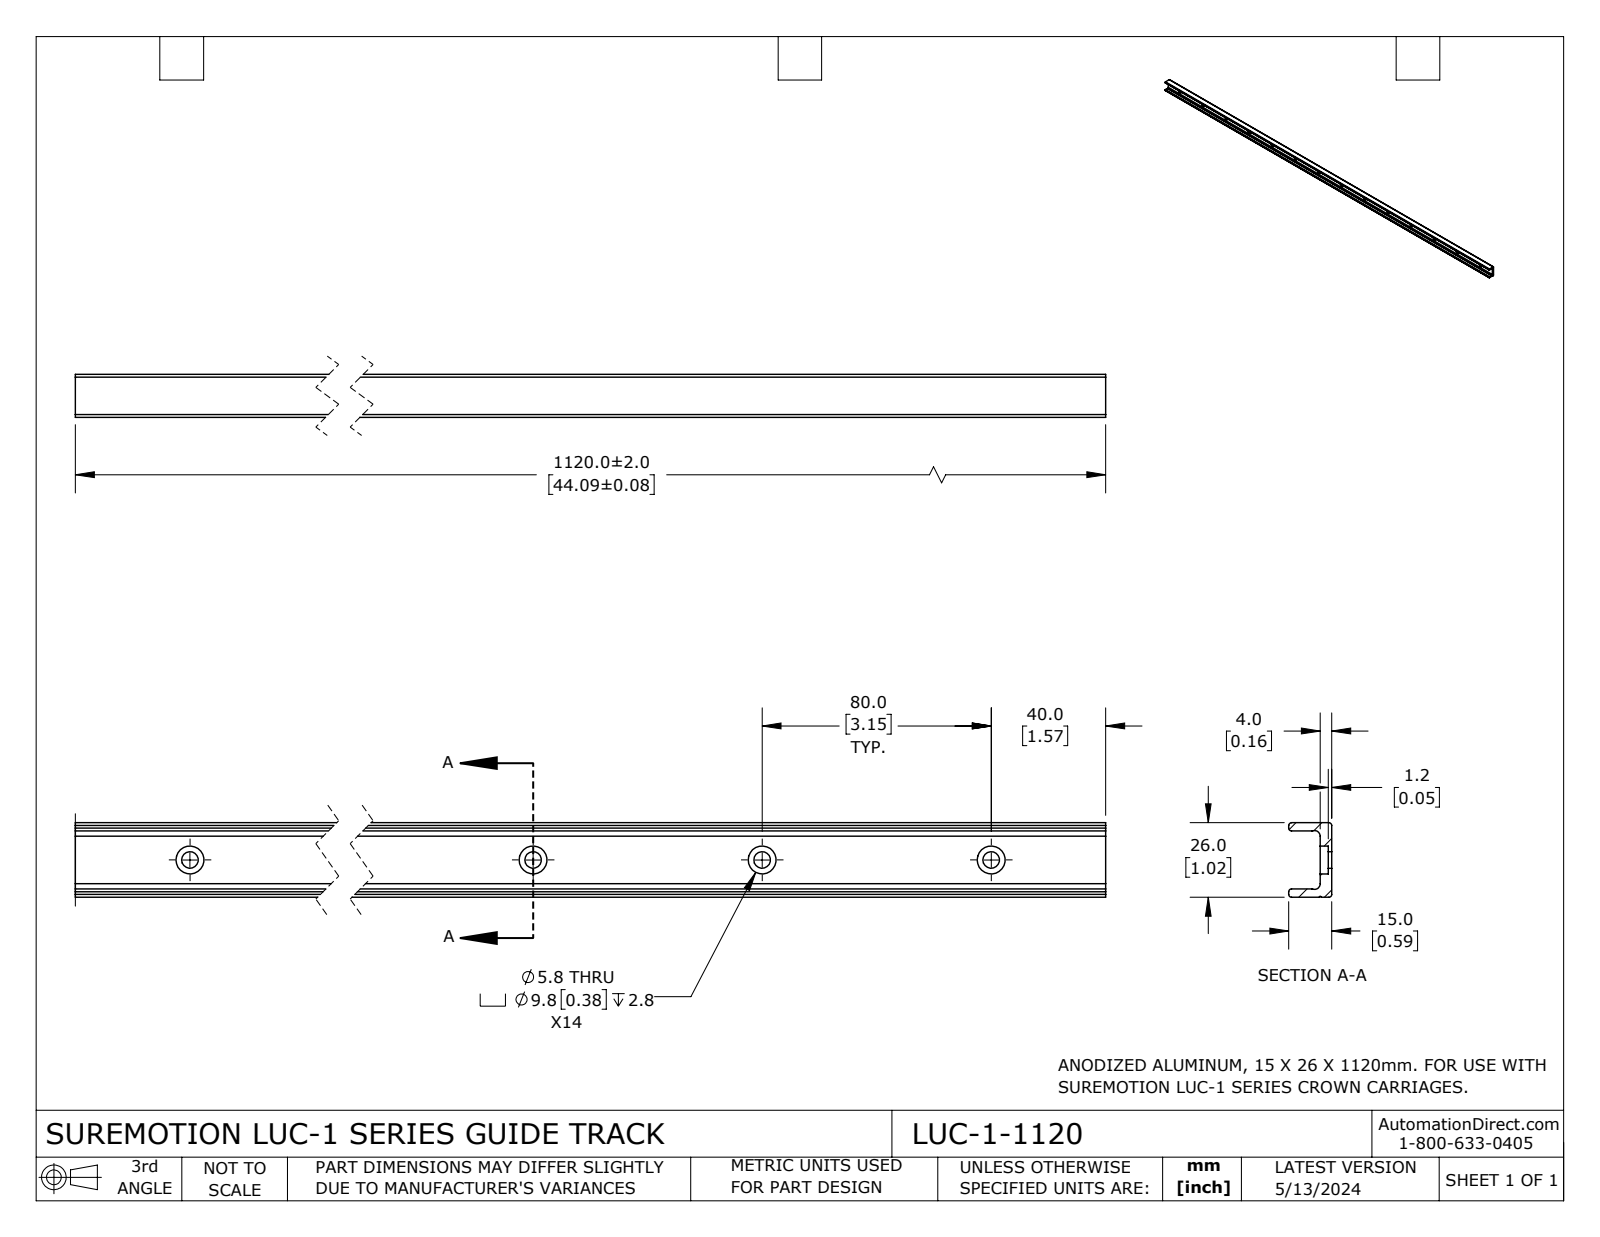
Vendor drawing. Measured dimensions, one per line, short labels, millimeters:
name: LUC-1-1120
written by: SolidWorks 2023 (CONFIG_CONTROL_DESIGN)
unit: mm
bodies: 1 solid, 92 faces (25 planar, 67 cylindrical, 0 other)
size: 1120 × 26.01 × 15.01
volume: 184 212 mm³; area: 113 665 mm²
holes: 14× ⌀5.79, 14× ⌀9.75
rounds: 8× R0.99, 2× R1.98, 1× R0.33
face distances: 4.01, 2.9, 23.12, 26.02, 20.22, 15.02, 11.01, 1.21, 2.8, 13.81
hole spacings: 80, 160, 240, 320, 400, 480, 560, 640
